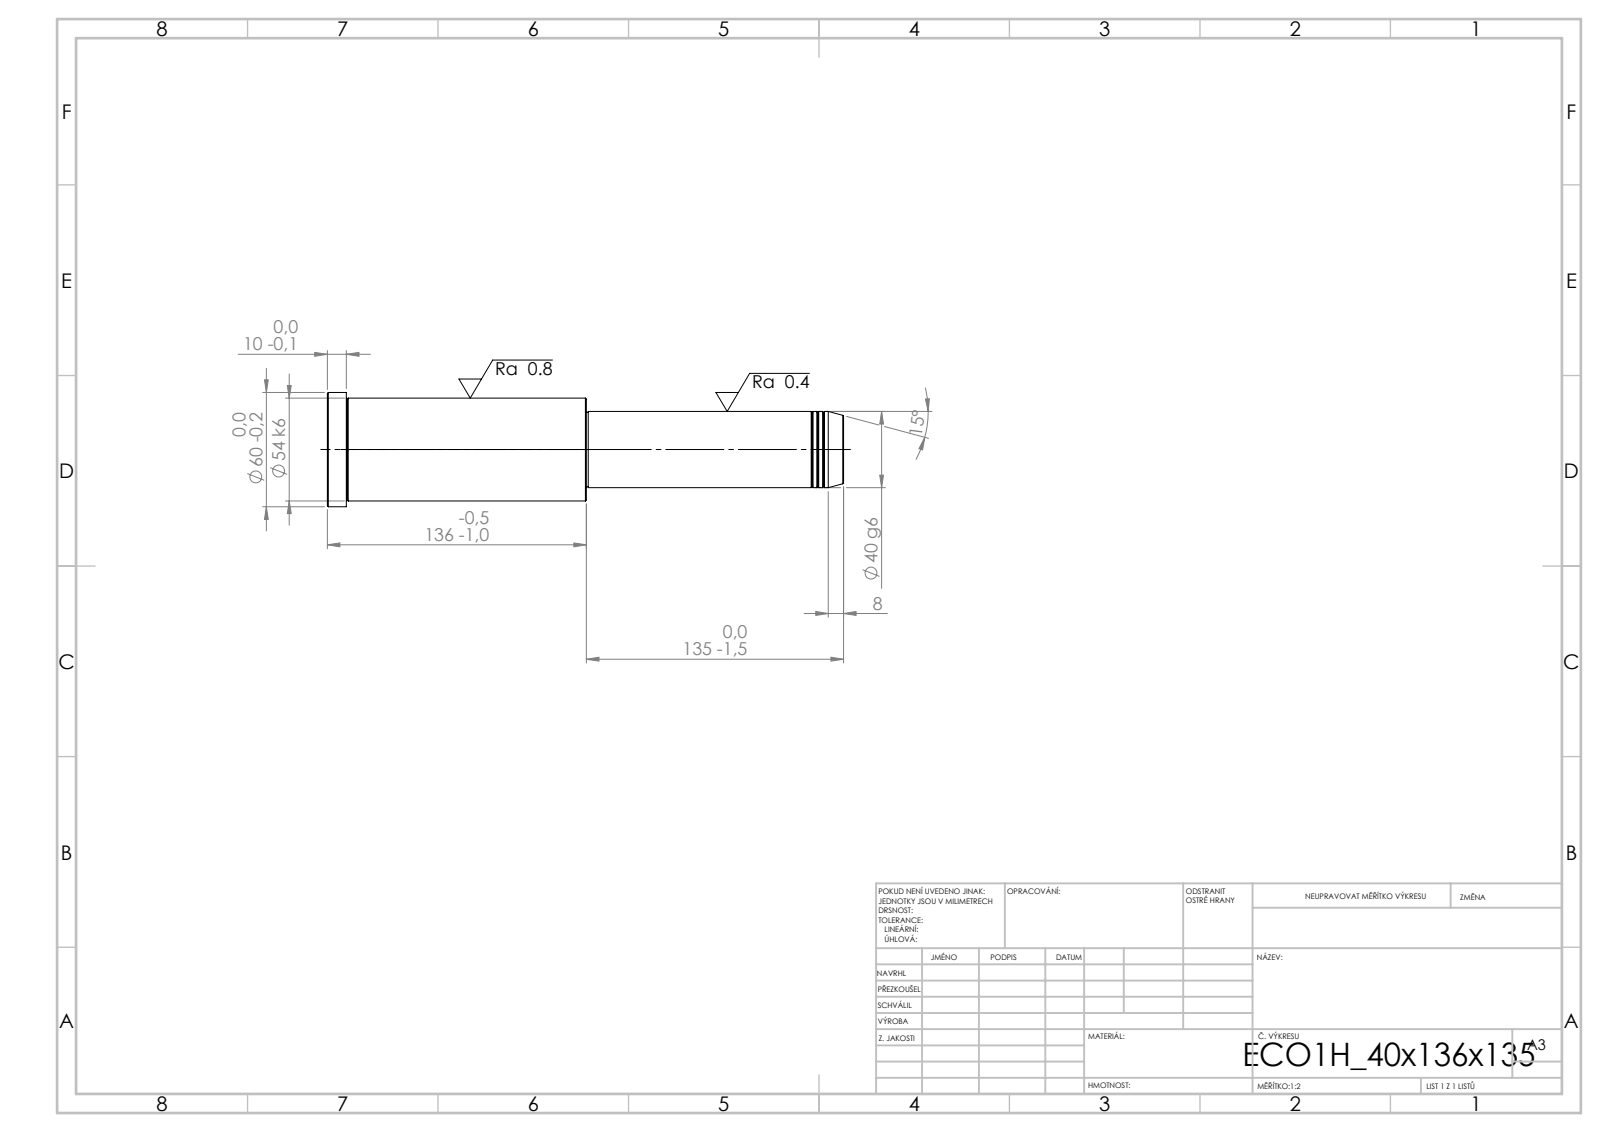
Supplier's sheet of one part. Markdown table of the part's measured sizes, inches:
| quantity | value |
| --- | --- |
| STEP written by | SolidWorks 2019 (CONFIG_CONTROL_DESIGN) |
| units | inches |
| bodies | 1 solid, 43 faces (5 planar, 14 cylindrical, 24 other) |
| overall size | 10.669 × 2.362 × 2.362 |
| volume | 29.6 in³ |
| surface area | 71.16 in² |
| round bosses / shafts (diameter × count) | 2.362 × 1, 2.126 × 1, 1.575 × 1, 1.535 × 1 |
| main face-to-face distances | 5.354, 5.315, 10.669, 10.276, 4.961, 0.394, 5.276, 0.039, 5, 5.394 |
